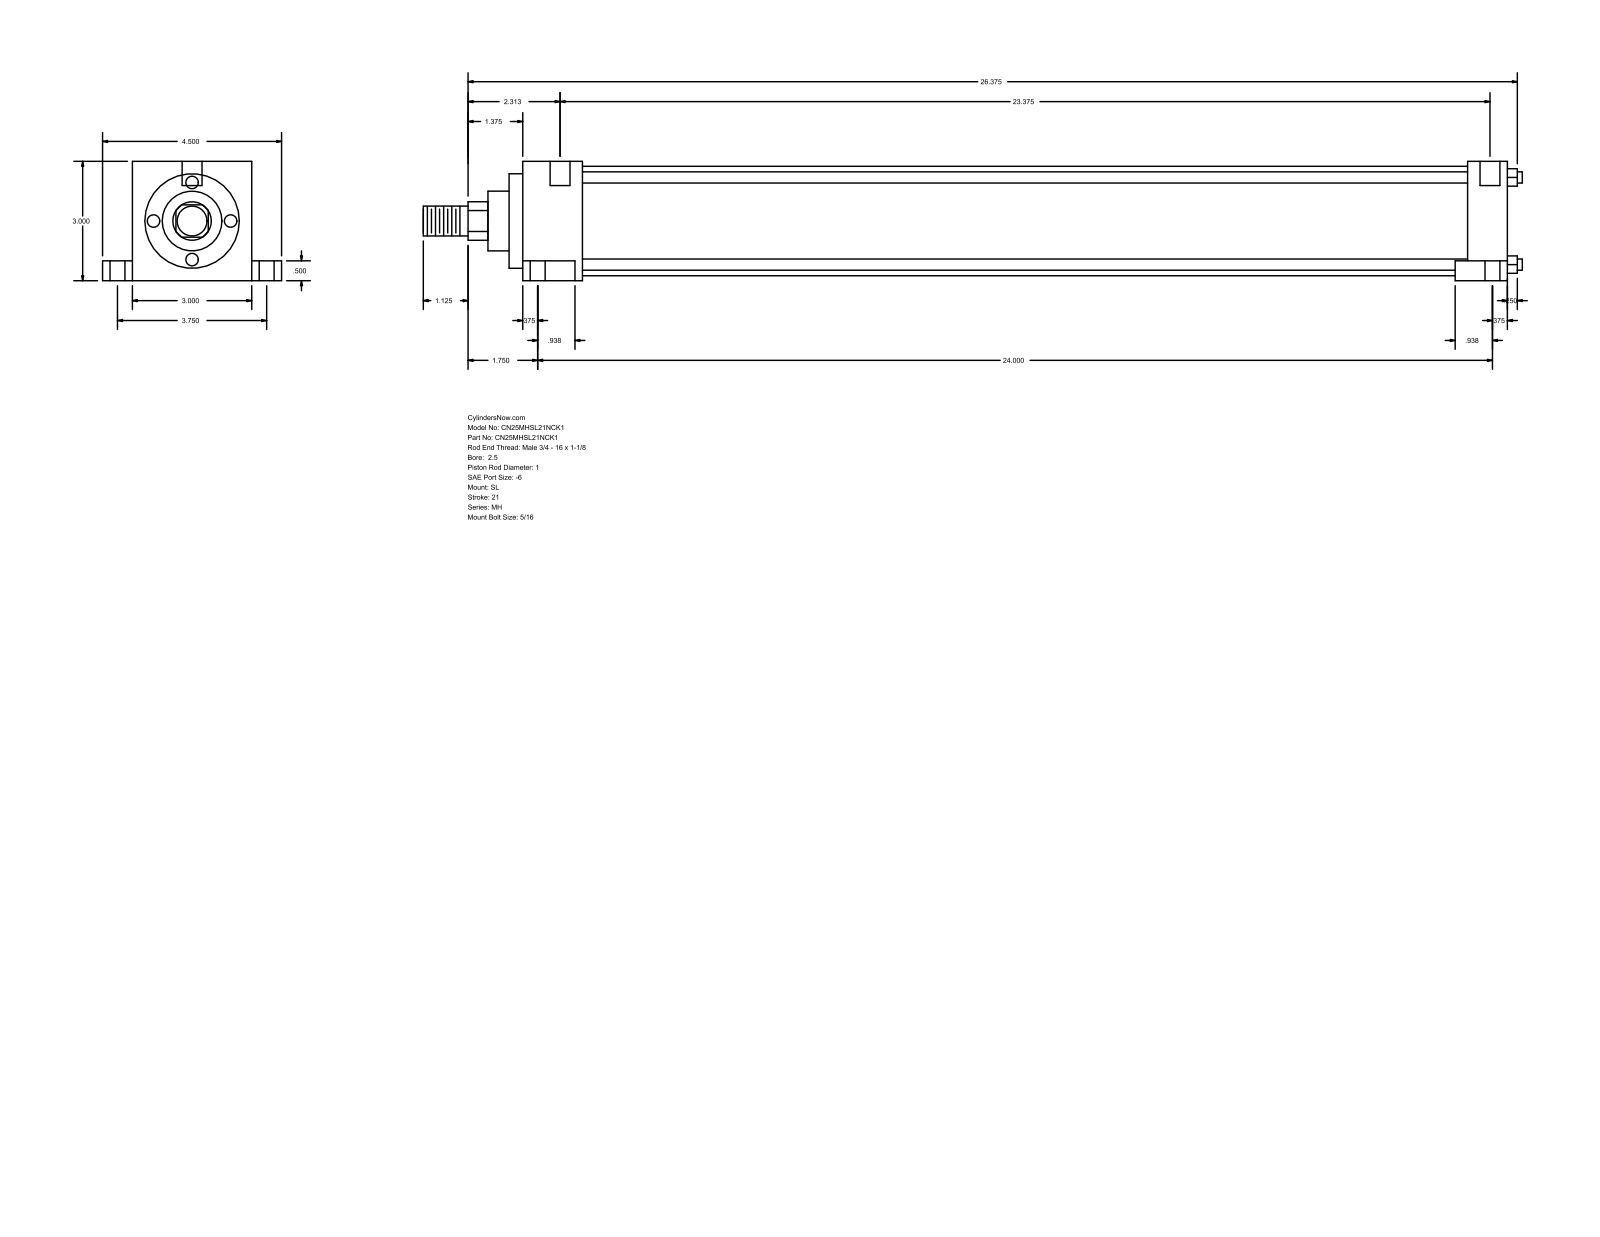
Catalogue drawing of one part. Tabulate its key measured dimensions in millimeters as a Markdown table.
| quantity | value |
| --- | --- |
| part name | MH_SL__0250_1 |
| STEP written by | GSSL Pune (CONFIG_CONTROL_DESIGN) |
| units | millimeters |
| bodies | 0 solids, 86 faces (61 planar, 25 cylindrical, 0 other) |
| overall size | 701.67 × 114.3 × 76.2 |
| round holes (diameter × count) | 5.56 × 2, 9.53 × 2, 15.88 × 2, 12.7 × 1 |
| round bosses / shafts (diameter × count) | 7.14 × 4, 69.85 × 1, 60.33 × 1, 38.1 × 1, 25.4 × 1, 19.05 × 1 |
| partial cylindrical surfaces (radius × count) | 12.29 × 1 |
| main face-to-face distances | 76.2, 25.41, 611.98, 637.39, 12.7, 63.5, 19.05, 95.25, 13.49, 625.47 |
| hole center spacings | 47.65, 3.18, 95.24 |
